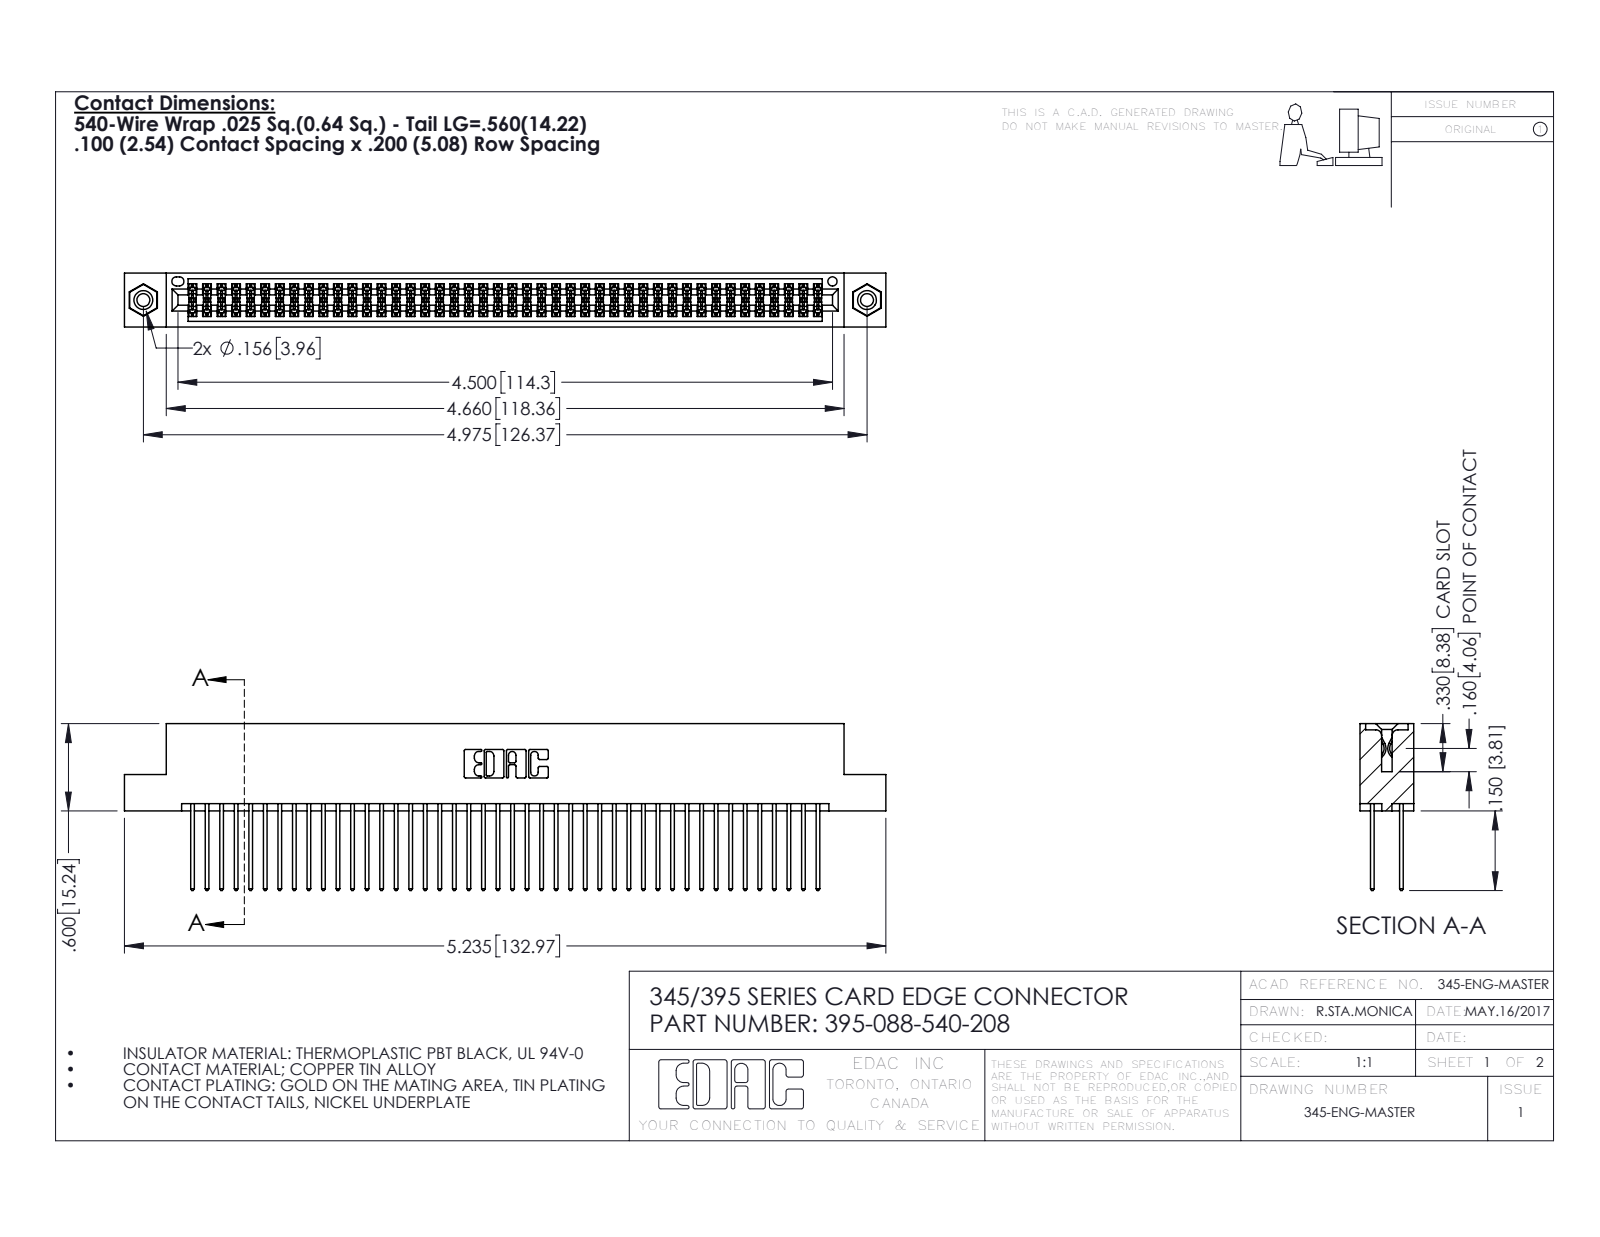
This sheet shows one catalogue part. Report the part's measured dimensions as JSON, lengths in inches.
{"part_name": "345-292-001_345-293-140; 345-250-001_345-250-003-102; 345 Part_Flush Mounting Lugs - 0.156 Dia-TI; 395-088-540-208", "step_written_by": "SolidWorks 2016 (CONFIG_CONTROL_DESIGN)", "units": "inches", "bodies": {"solids": 91, "faces": 4586, "planar": 3016, "cylindrical": 1554, "other": 16}, "overall_size": [5.235, 1.147, 0.37], "volume_in3": 0.809, "surface_area_in2": 32.87, "round_holes": [[0.089, 2], [0.125, 2], [0.156, 2], [0.064, 1]], "round_bosses_or_shafts": [[0.155, 2]], "partial_cylinders_radius": [[0.006, 132], [0.01, 88], [0.01, 22], [0.007, 6], [0.031, 6], [0.026, 3], [0.014, 2], [0.019, 2]], "face_to_face_distances": [0.072, 0.298, 0.2, 0.098, 0.272, 0.025, 0.37, 0.225, 0.175, 0.149], "hole_center_spacings": [0.27, 4.739, 4.975]}
